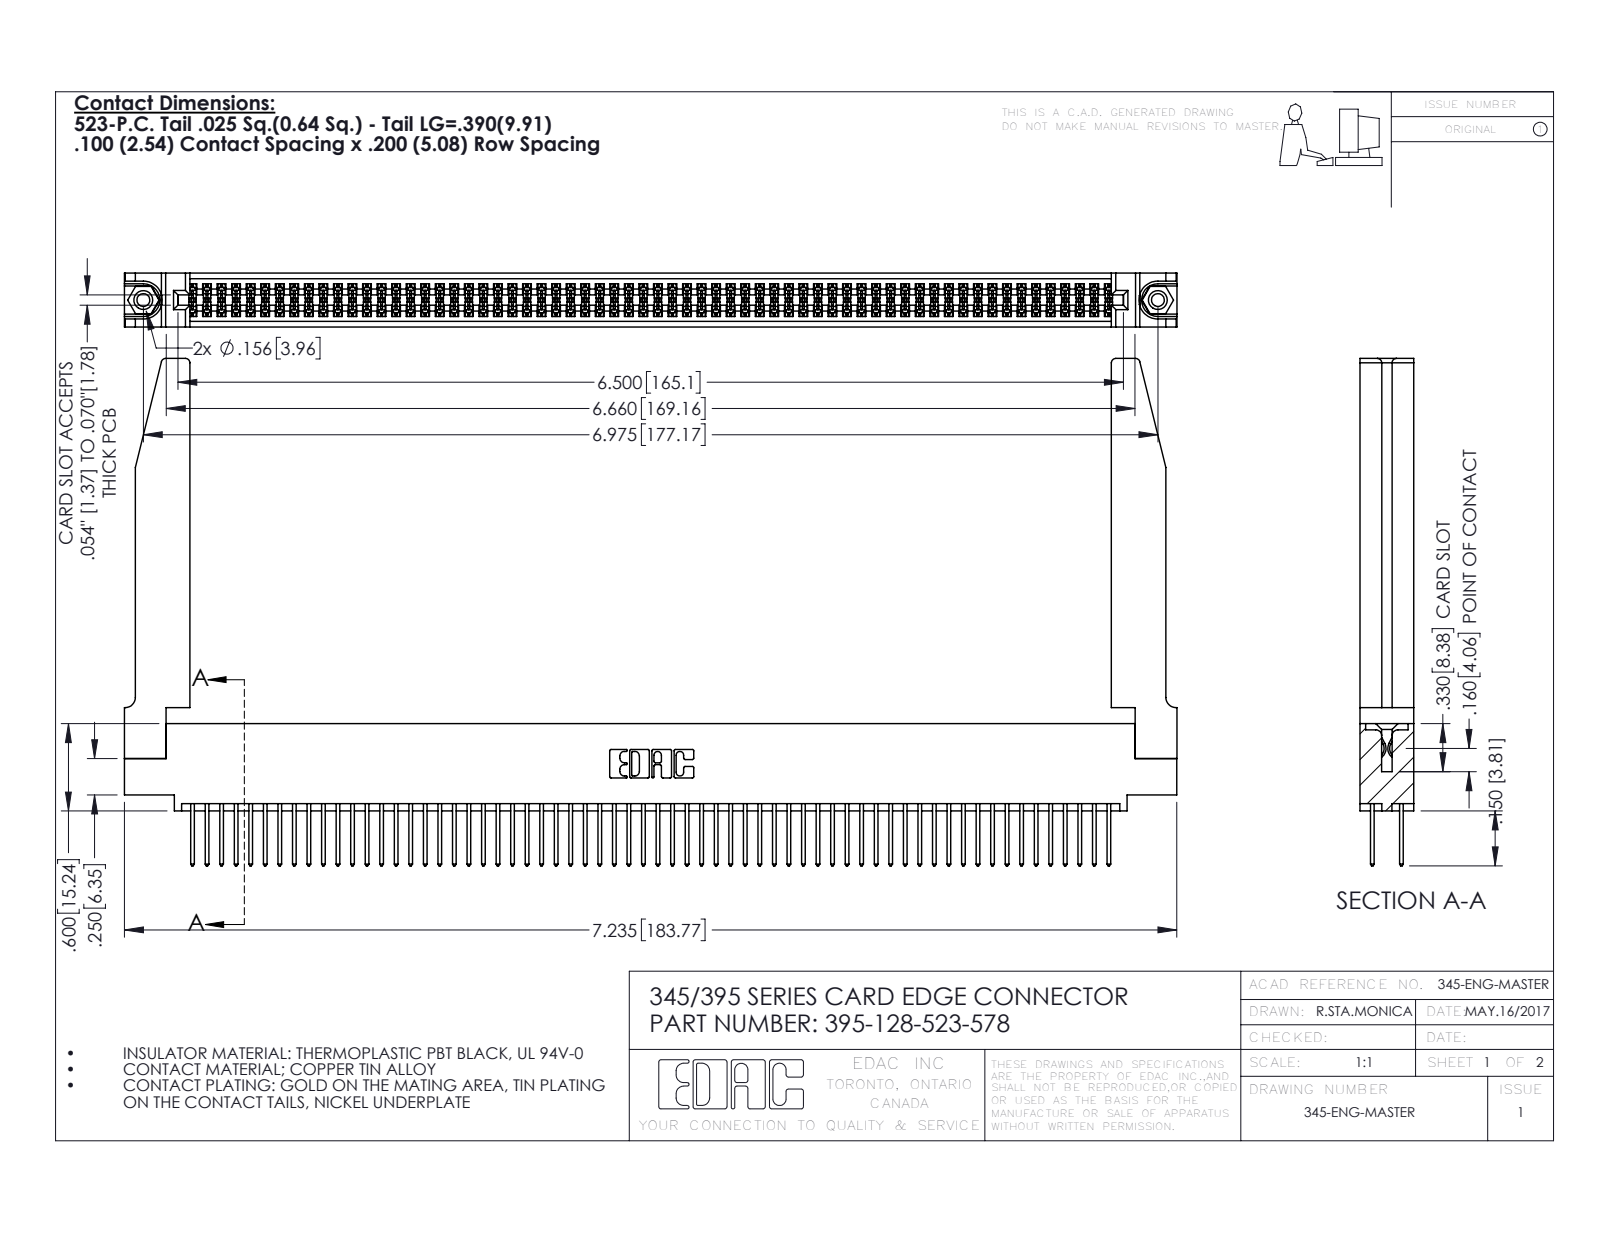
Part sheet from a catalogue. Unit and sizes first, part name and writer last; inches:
Units: inches
Overall size (bounding box): 7.236 × 3.487 × 0.37
Round holes (diameter × count): ⌀0.089 ×2, ⌀0.125 ×2, ⌀0.156 ×2, ⌀0.064 ×1
Round bosses / shafts (diameter × count): ⌀0.155 ×2
Partial cylindrical surfaces — rounded edges, fillets, slot ends (radius × count): R0.006 ×192, R0.01 ×128, R0.01 ×22, R0.03 ×8, R0.007 ×6, R0.031 ×6, R0.026 ×3, R0.014 ×2
Main face-to-face distances: 0.072, 0.298, 0.37, 0.098, 0.272, 0.025, 0.2, 0.225, 0.175, 0.148
Hole centre spacings: 0.27, 6.739, 6.975
Volume: 1.588 in³ · Surface area: 55.04 in²
Bodies: 133 solids, 6764 faces (4450 planar, 2262 cylindrical, 52 other)
Part name (STEP PRODUCT): 345-220-078_345-220-078; 345-250-001_345-250-001-102; 395-128-523-578; 345 Part_0.110 Offset - 0.156 Dia-TH (+1 more)
STEP written by: SolidWorks 2016 (CONFIG_CONTROL_DESIGN)
